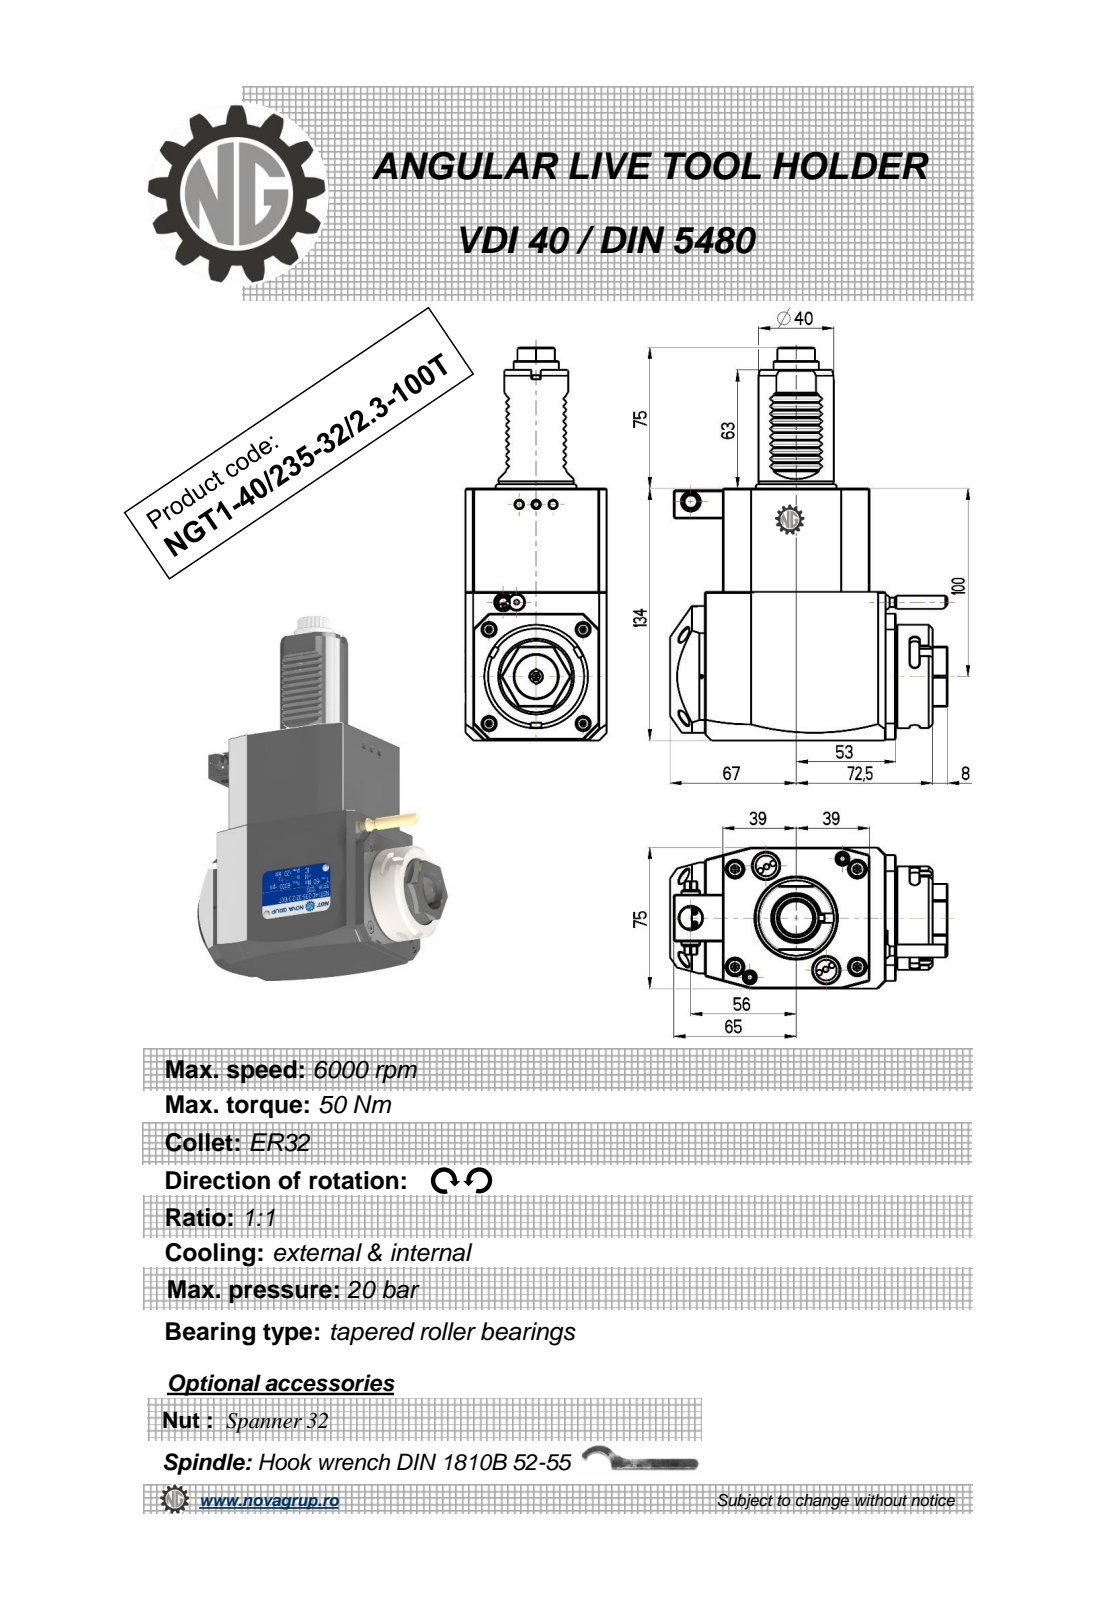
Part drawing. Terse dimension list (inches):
name: NGT1_40_235_32_1_3_100T
written by: PRO/ENGINEER BY PARAMETRIC TECHNOLOGY CORPORATION, 2010280 (CONFIG_CONTROL_DESIGN)
unit: in
bodies: 1 solid, 536 faces (232 planar, 194 cylindrical, 110 other)
size: 8.228 × 5.807 × 2.953
volume: 65.6 in³; area: 122.2 in²
holes: 2× ⌀0.13, 2× ⌀0.177, 2× ⌀0.295, 1× ⌀0.098, 1× ⌀0.118, 1× ⌀0.374, 1× ⌀0.472, 1× ⌀0.906
bosses: 2× ⌀0.315, 1× ⌀2.165, 1× ⌀1.89, 1× ⌀1.575, 1× ⌀0.945, 1× ⌀0.394, 1× ⌀0.276, 1× ⌀0.197
rounds: 48× R0.082, 20× R0.012, 6× R0.098, 2× R7.087, 1× R0.152, 1× R0.167, 1× R0.357, 1× R0.391
face distances: 2.953, 5.276, 3.071, 0.551, 3.622, 3.11, 0.984, 3.342, 0.768, 4.39
hole spacings: 1.225, 0.711, 1.701, 2.16, 2.45, 2.87, 2.878, 3.602
